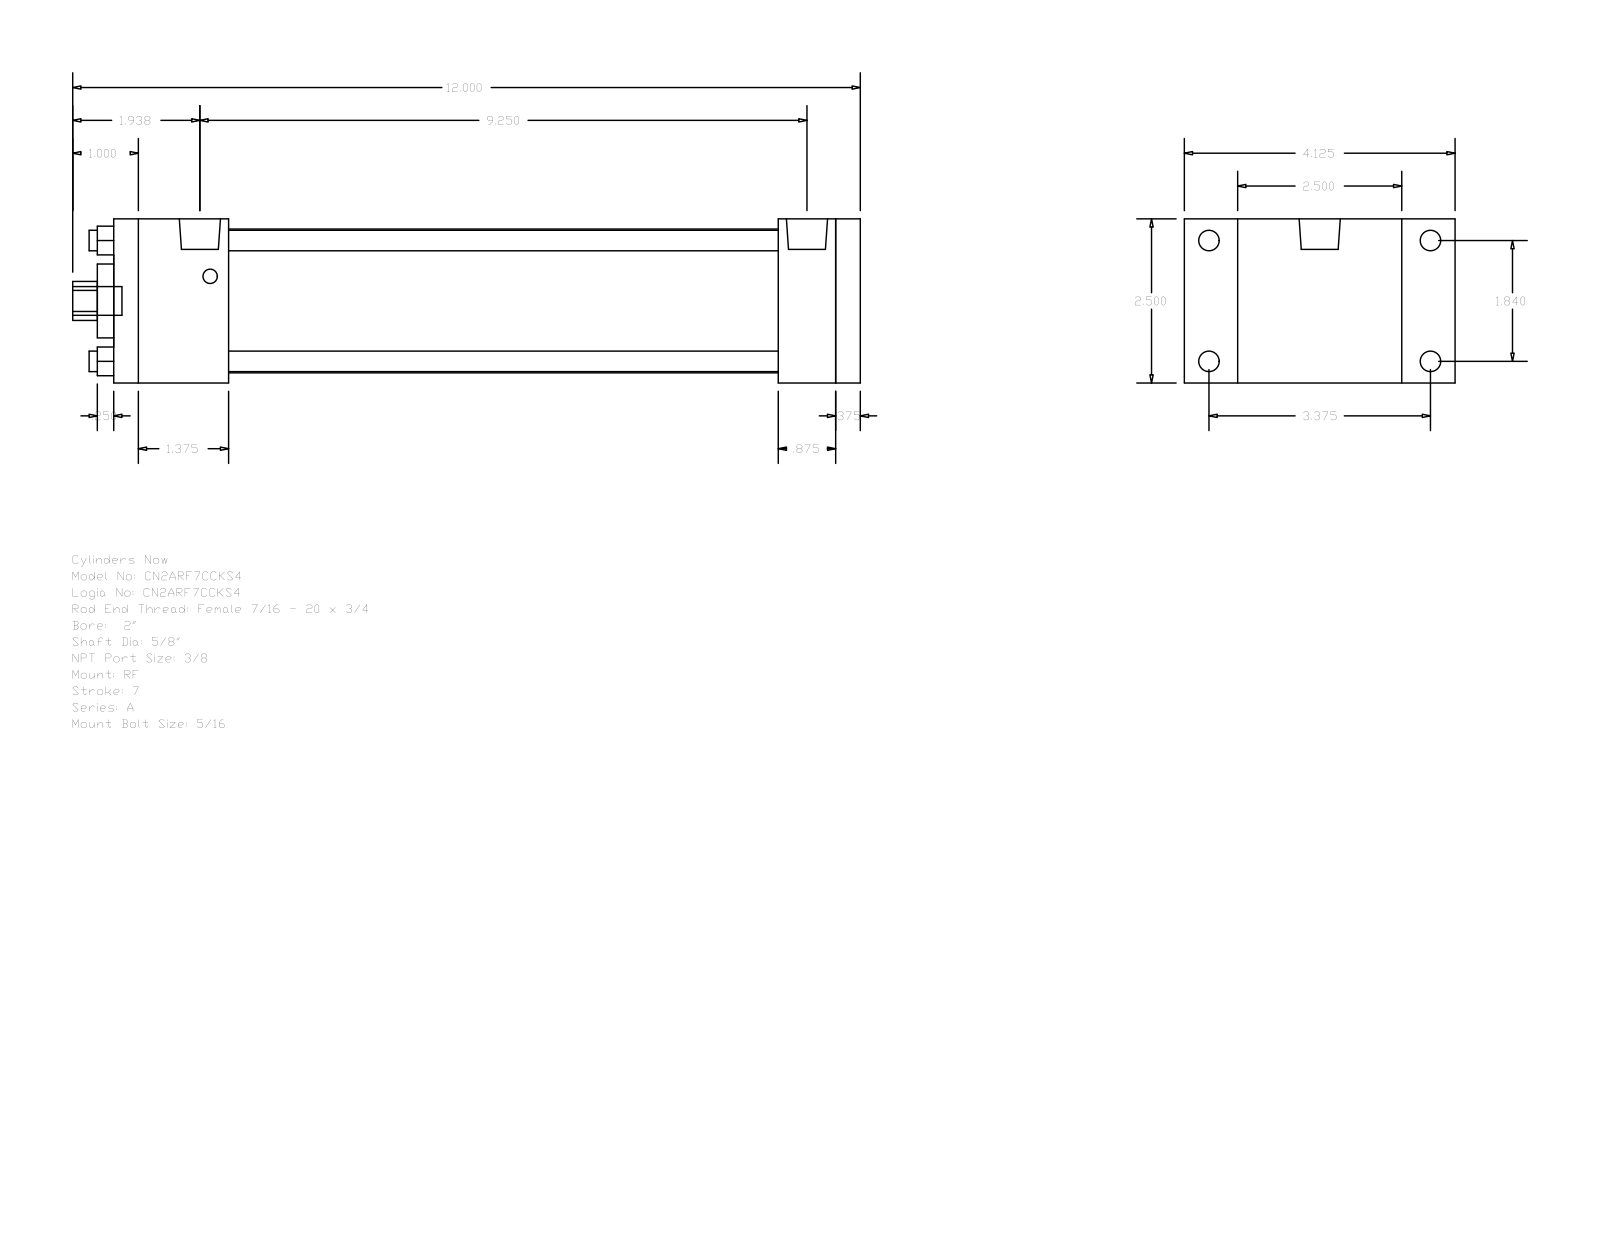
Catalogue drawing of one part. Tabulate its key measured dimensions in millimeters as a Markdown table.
| quantity | value |
| --- | --- |
| part name | A_RF__0200_0.625 |
| STEP written by | GSSL Pune (CONFIG_CONTROL_DESIGN) |
| units | millimeters |
| bodies | 0 solids, 92 faces (64 planar, 28 cylindrical, 0 other) |
| overall size | 304.8 × 104.78 × 63.5 |
| round holes (diameter × count) | 7.94 × 4, 15.88 × 1, 28.57 × 1, 55.63 × 1 |
| round bosses / shafts (diameter × count) | 7.94 × 4, 5.56 × 4, 15.93 × 2, 11.11 × 1 |
| partial cylindrical surfaces (radius × count) | 7.54 × 1 |
| main face-to-face distances | 63.5, 288.92, 9.53, 279.39, 44.45, 234.94, 244.47, 257.17, 212.72, 22.22 |
| hole center spacings | 33.05, 46.74, 66.1 |
